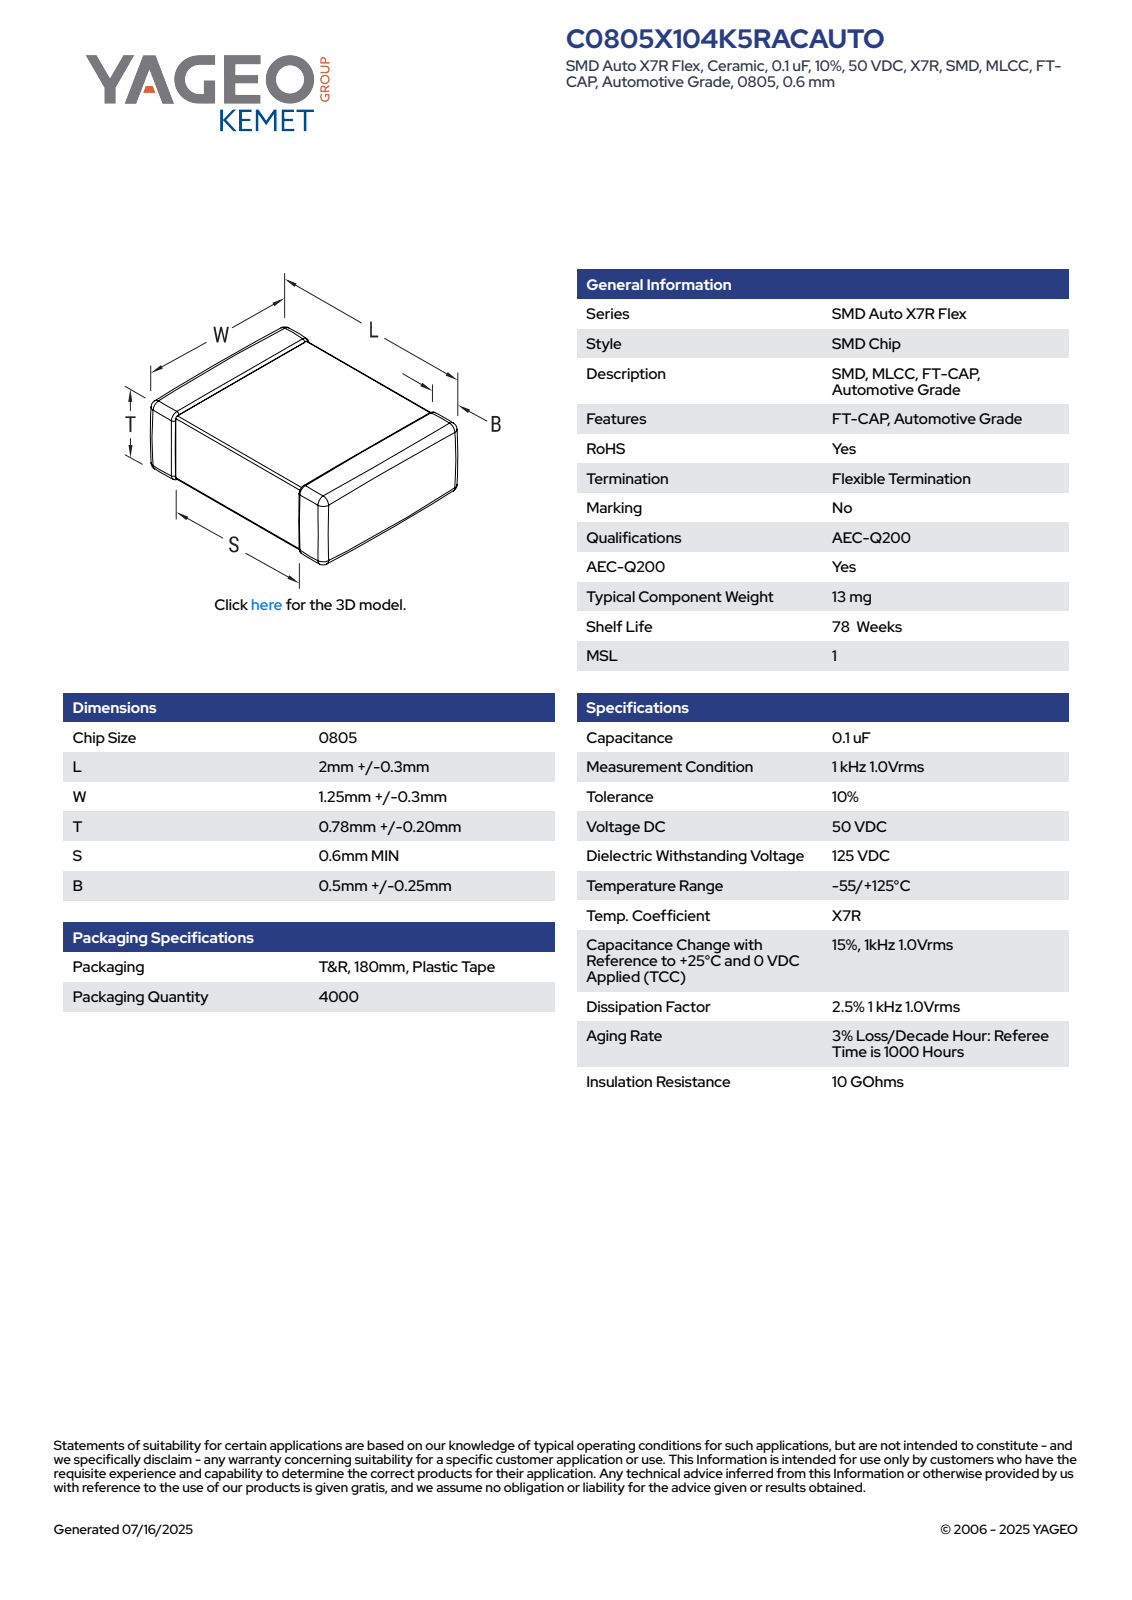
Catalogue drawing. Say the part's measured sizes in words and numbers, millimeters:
The part is named "CCS_CCSTD_0805_L2.3W1.55T0.98B0.5". Its 3-D file was written by "SolidWorks 2014 (AUTOMOTIVE_DESIGN)". It is 4 solids with 125 faces: 71 planar, 38 cylindrical and 16 other. Overall it measures 2.3 by 1.55 by 0.98 millimeters. Its volume is 3 cubic millimeters and its surface area 15 square millimeters. The main face-to-face distances are 0.95, 0.92, 1.52, 2.3, 0.98, 1.49, 1.55, 1.06, 1.24, 1.01.
